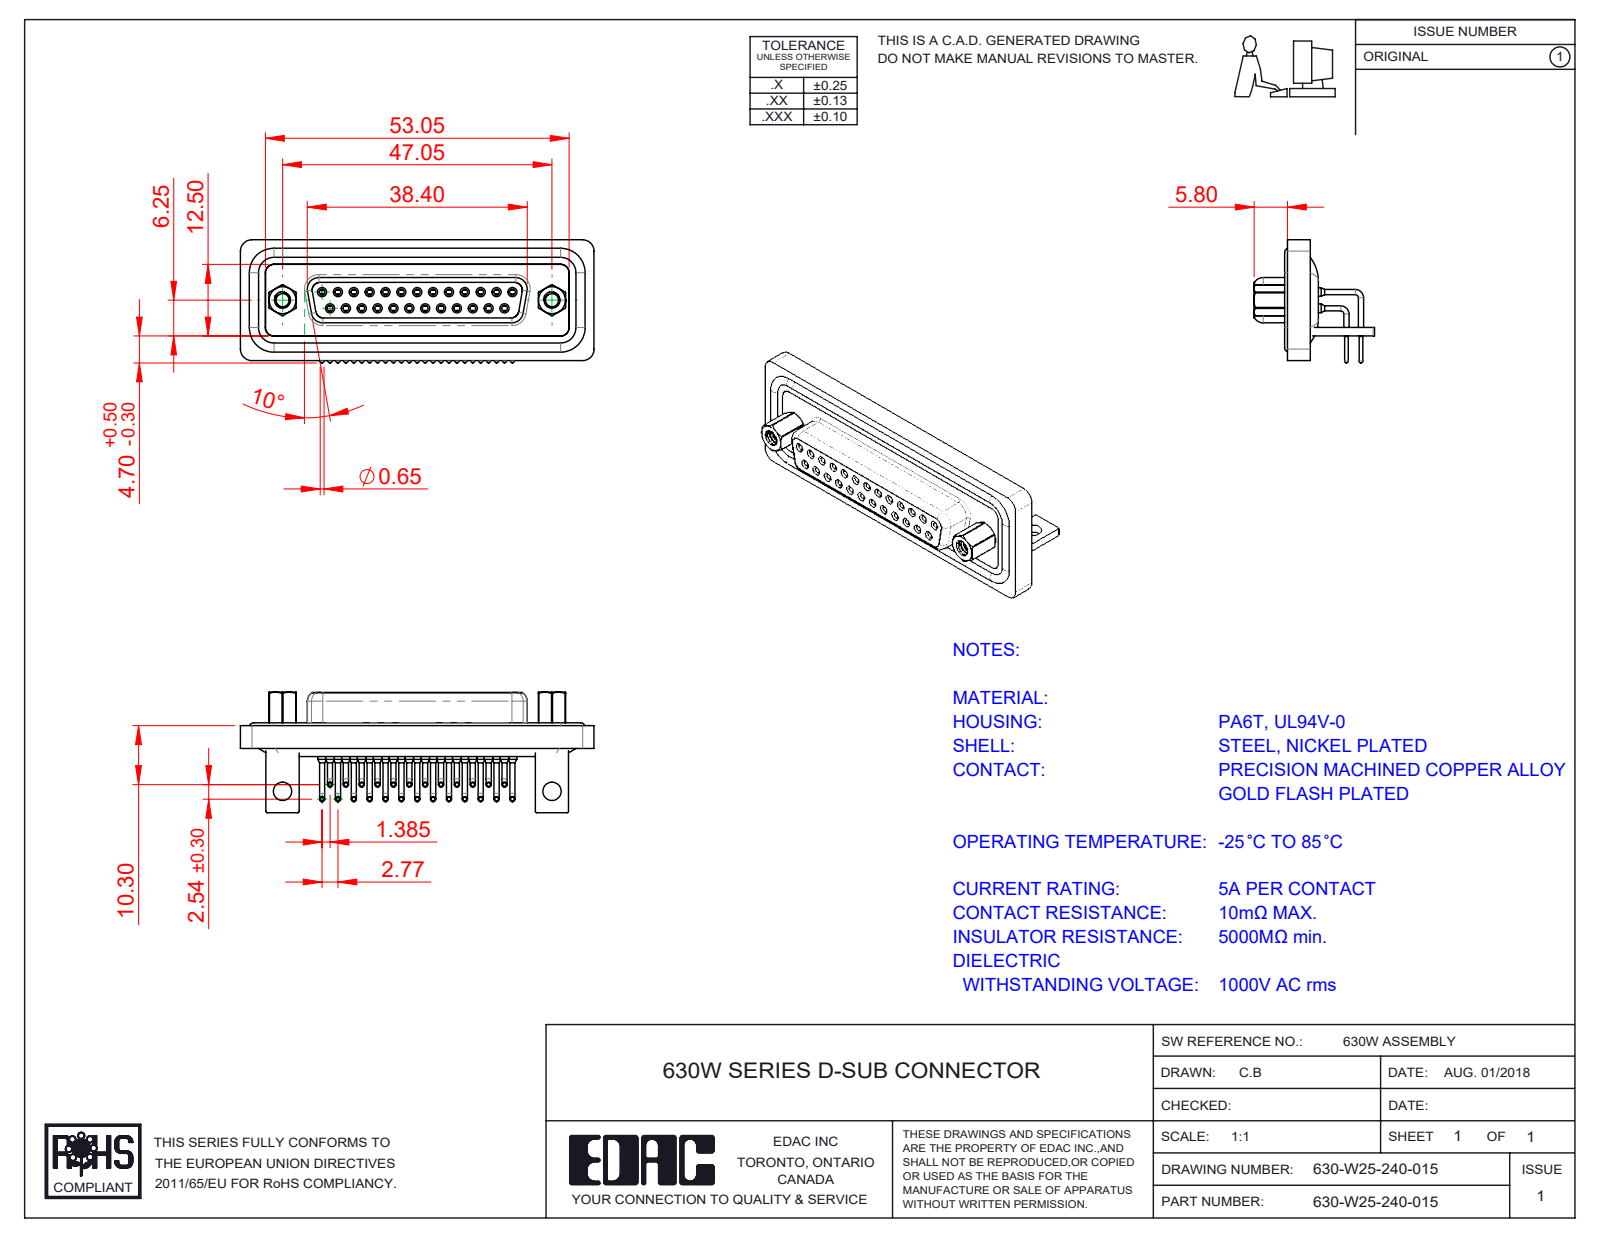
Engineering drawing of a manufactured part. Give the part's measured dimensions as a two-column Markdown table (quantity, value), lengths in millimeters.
| quantity | value |
| --- | --- |
| part name | 630W Waterproof Housing_25 Contacts; 630W Contact Row 2; 630W Stabilizer Bracket; 630W Shell_25 Contacts (+5 more) |
| STEP written by | SolidWorks 2016 (CONFIG_CONTROL_DESIGN) |
| units | millimeters |
| bodies | 35 solids, 1844 faces (498 planar, 865 cylindrical, 481 other) |
| overall size | 61.74 × 21.5 × 21.05 |
| volume | 7 783 mm³ |
| surface area | 14 152 mm² |
| round holes (diameter × count) | 1 × 25, 1.1 × 25, 1.5 × 25, 1.7 × 25, 1.8 × 25, 2 × 25, 2.26 × 2, 2.29 × 2, 3.2 × 2, 4 × 2, 4.8 × 2, 4.9 × 2 |
| round bosses / shafts (diameter × count) | 0.9 × 50, 1.6 × 29, 0.65 × 25, 2.79 × 2, 5 × 1 |
| partial cylindrical surfaces (radius × count) | 2 × 15, 1.5 × 14, 0.25 × 12, 1.35 × 8, 2.7 × 6, 0.5 × 5, 0.9 × 4, 1.6 × 4 |
| main face-to-face distances | 0.4, 1.8, 1.6, 9.8, 1.1, 2.9, 2.5, 7.45, 13.65, 1.35 |
| hole center spacings | 3.16, 2.77, 5.54, 8.31, 11.08, 13.85, 16.62, 5.03 |
